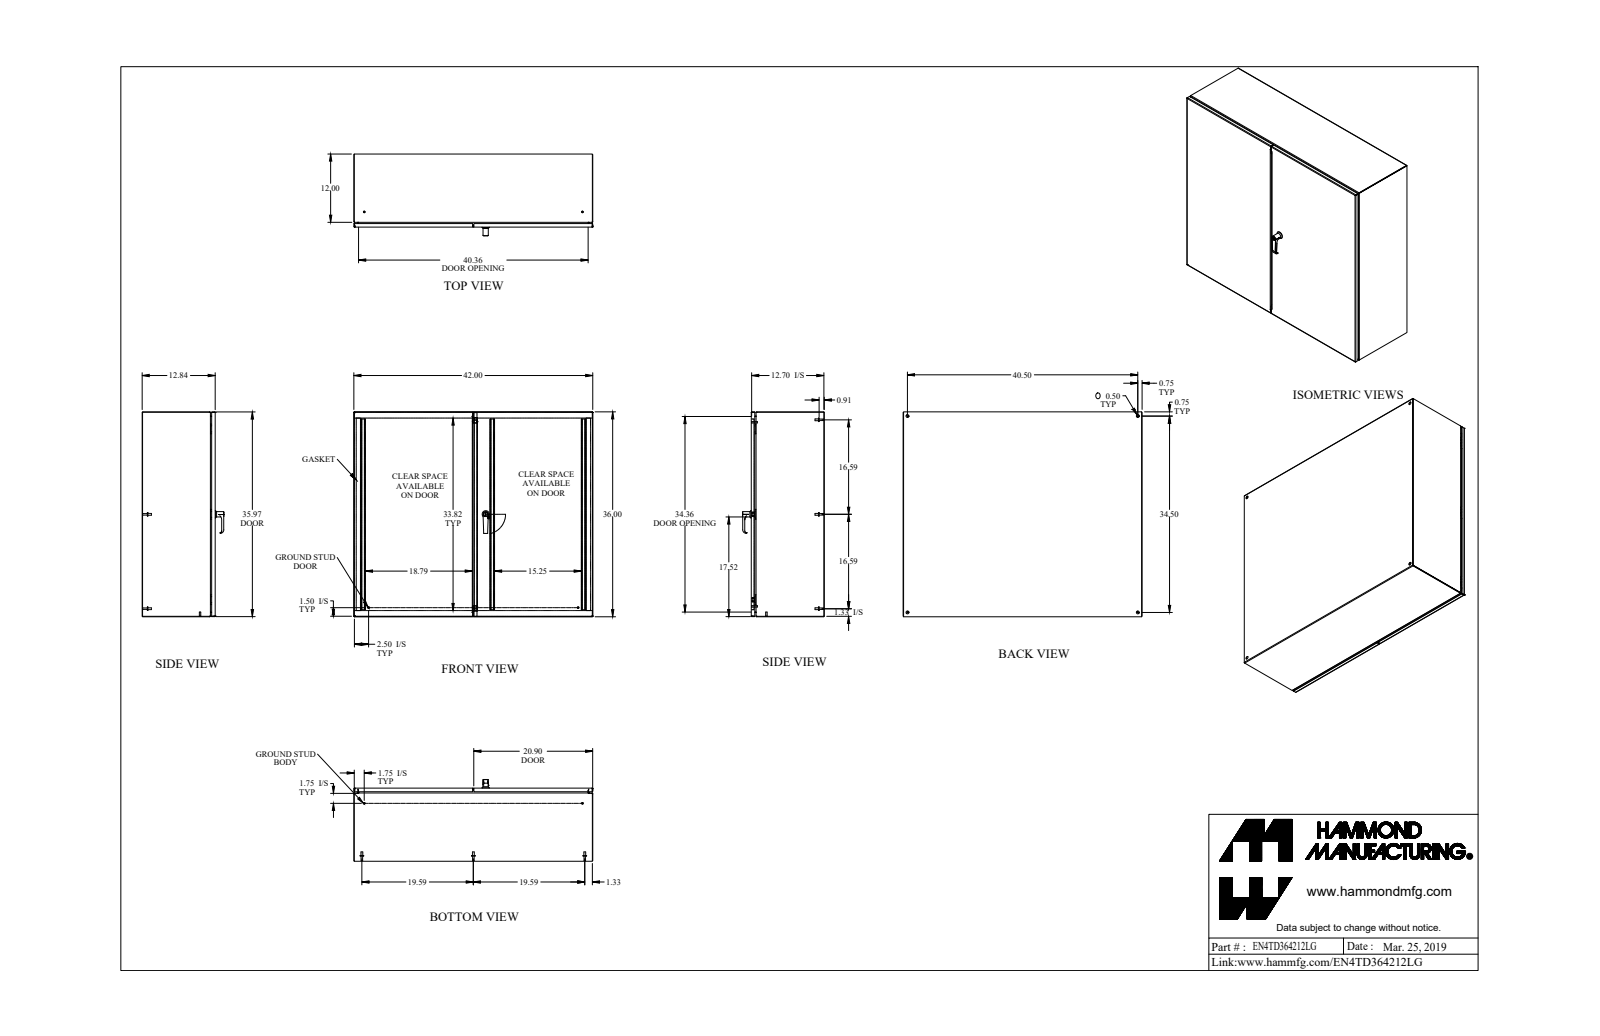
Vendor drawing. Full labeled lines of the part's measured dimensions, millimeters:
Part name (STEP PRODUCT): EN4TD364212LG
STEP written by: SolidWorks 2018 (AUTOMOTIVE_DESIGN)
Units: millimetres
Bodies: 87 solids, 2175 faces (967 planar, 802 cylindrical, 406 other)
Overall size (bounding box): 1066.8 × 914.4 × 365
Volume: 7 122 000 mm³ · Surface area: 7 413 000 mm²
Round holes (diameter × count): ⌀5 ×5, ⌀4.5 ×4, ⌀12.7 ×4, ⌀6.1 ×3, ⌀6.1 ×3, ⌀6.7 ×3, ⌀4.4 ×2, ⌀6.4 ×2, ⌀6.5 ×2, ⌀6.6 ×2, ⌀6.7 ×2, ⌀8 ×2
Round bosses / shafts (diameter × count): ⌀6.4 ×11, ⌀8 ×10, ⌀6.9 ×8, ⌀15.9 ×6, ⌀13 ×4, ⌀9.5 ×4, ⌀7.1 ×4, ⌀4 ×4
Partial cylindrical surfaces — rounded edges, fillets, slot ends (radius × count): R0.9 ×26, R2.7 ×26, R1.6 ×25, R2.4 ×20, R1.1 ×18, R2.1 ×18, R0.5 ×16, R0.4 ×15
Main face-to-face distances: 1.8, 324.4, 322.5, 326.2, 912.6, 1065, 910.7, 914.4, 1063.1, 1066.8
Hole centre spacings: 20, 578, 634.8, 718.5, 876.3, 1028.7, 1351.3, 20
